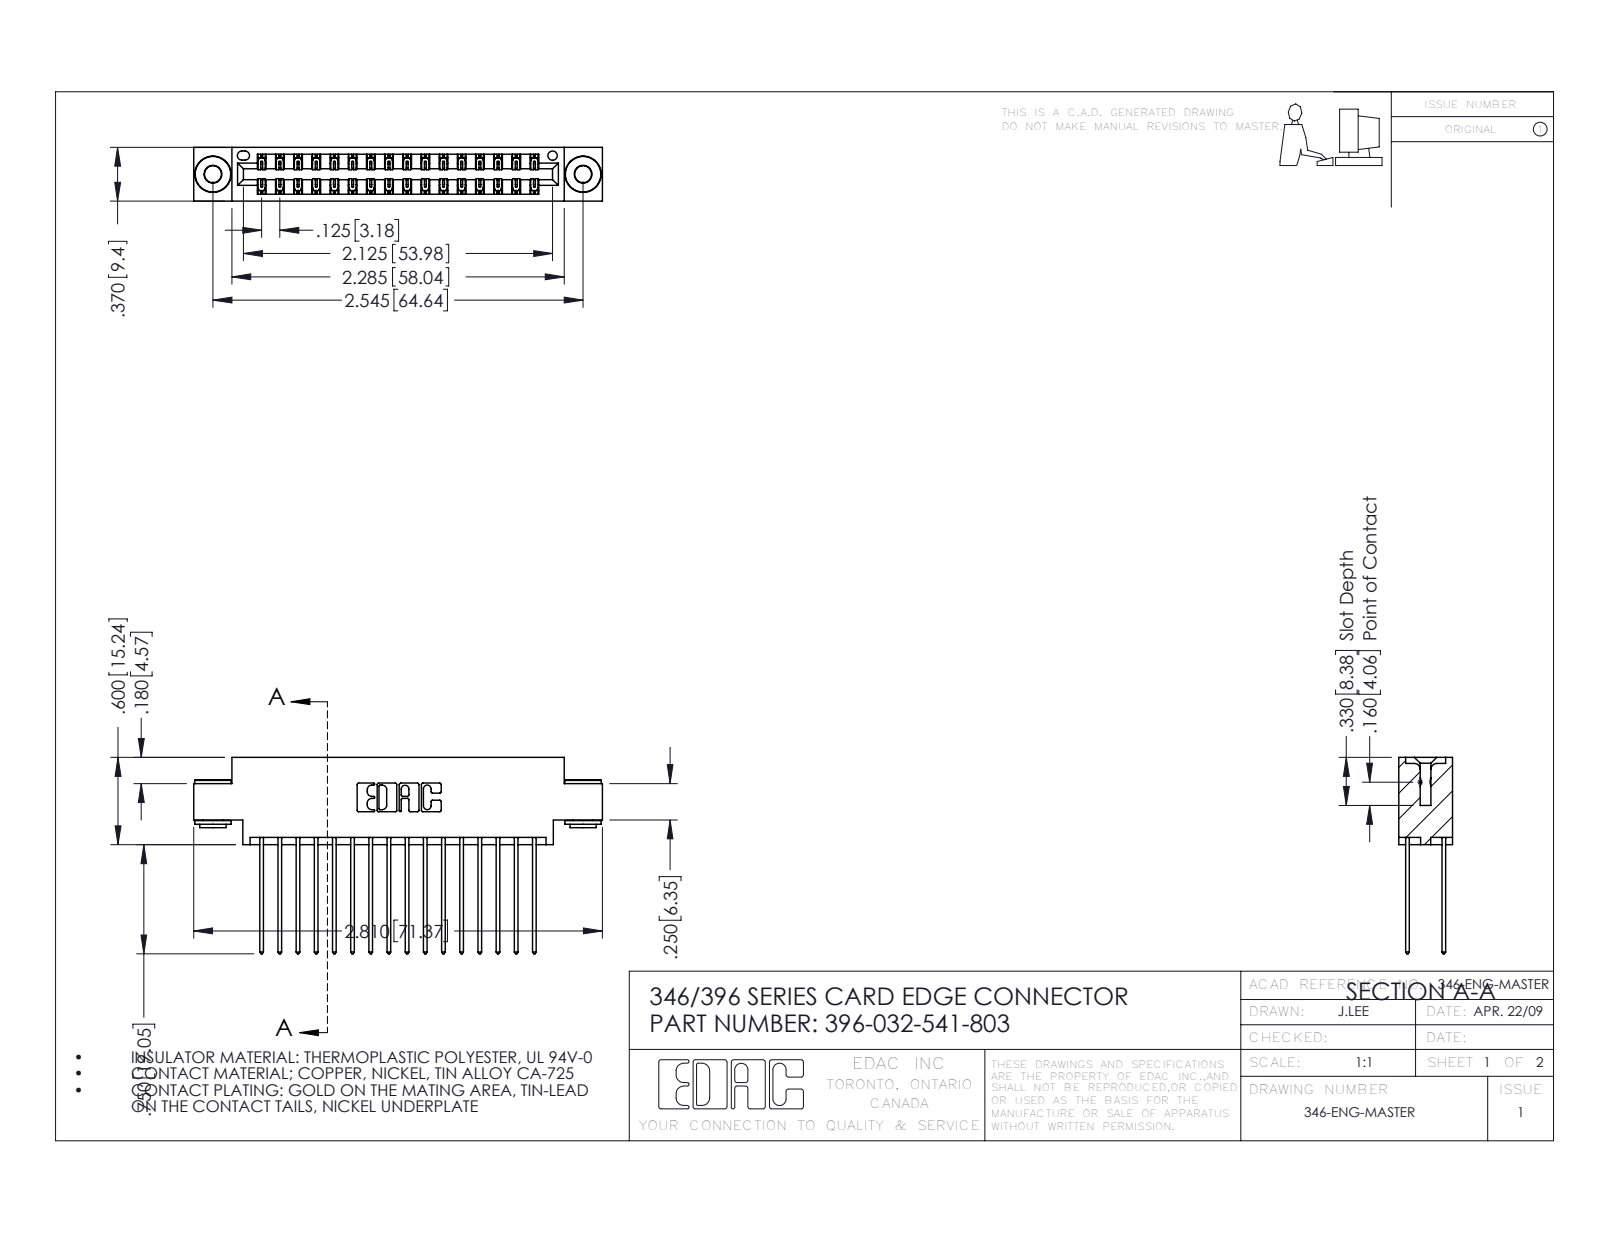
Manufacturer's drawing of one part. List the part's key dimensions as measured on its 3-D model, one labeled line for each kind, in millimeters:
Part name (STEP PRODUCT): 346 Part_0.170 Offset - 0.156 Dia-TH; 396-032-541-803; 345-292-001_345-293-141; 345-250-002_345-250-002-102
STEP written by: SolidWorks 2016 (CONFIG_CONTROL_DESIGN)
Units: millimetres
Bodies: 35 solids, 1828 faces (1210 planar, 610 cylindrical, 8 other)
Overall size (bounding box): 71.4 × 34.3 × 9.4
Volume: 6 800 mm³ · Surface area: 10 220 mm²
Round holes (diameter × count): ⌀2.9 ×2, ⌀4 ×2, ⌀1.6 ×1
Round bosses / shafts (diameter × count): ⌀6.4 ×2, ⌀4.6 ×2, ⌀3.5 ×2
Partial cylindrical surfaces — rounded edges, fillets, slot ends (radius × count): R0.2 ×48, R0.3 ×32, R0.3 ×22, R0.2 ×6, R0.8 ×6, R0.7 ×3, R0.4 ×2, R0.6 ×2
Main face-to-face distances: 1.2, 8.2, 6.4, 0.6, 9.4, 1.8, 7.6, 7, 5.7, 3.8
Hole centre spacings: 6.2, 59.4, 64.6
